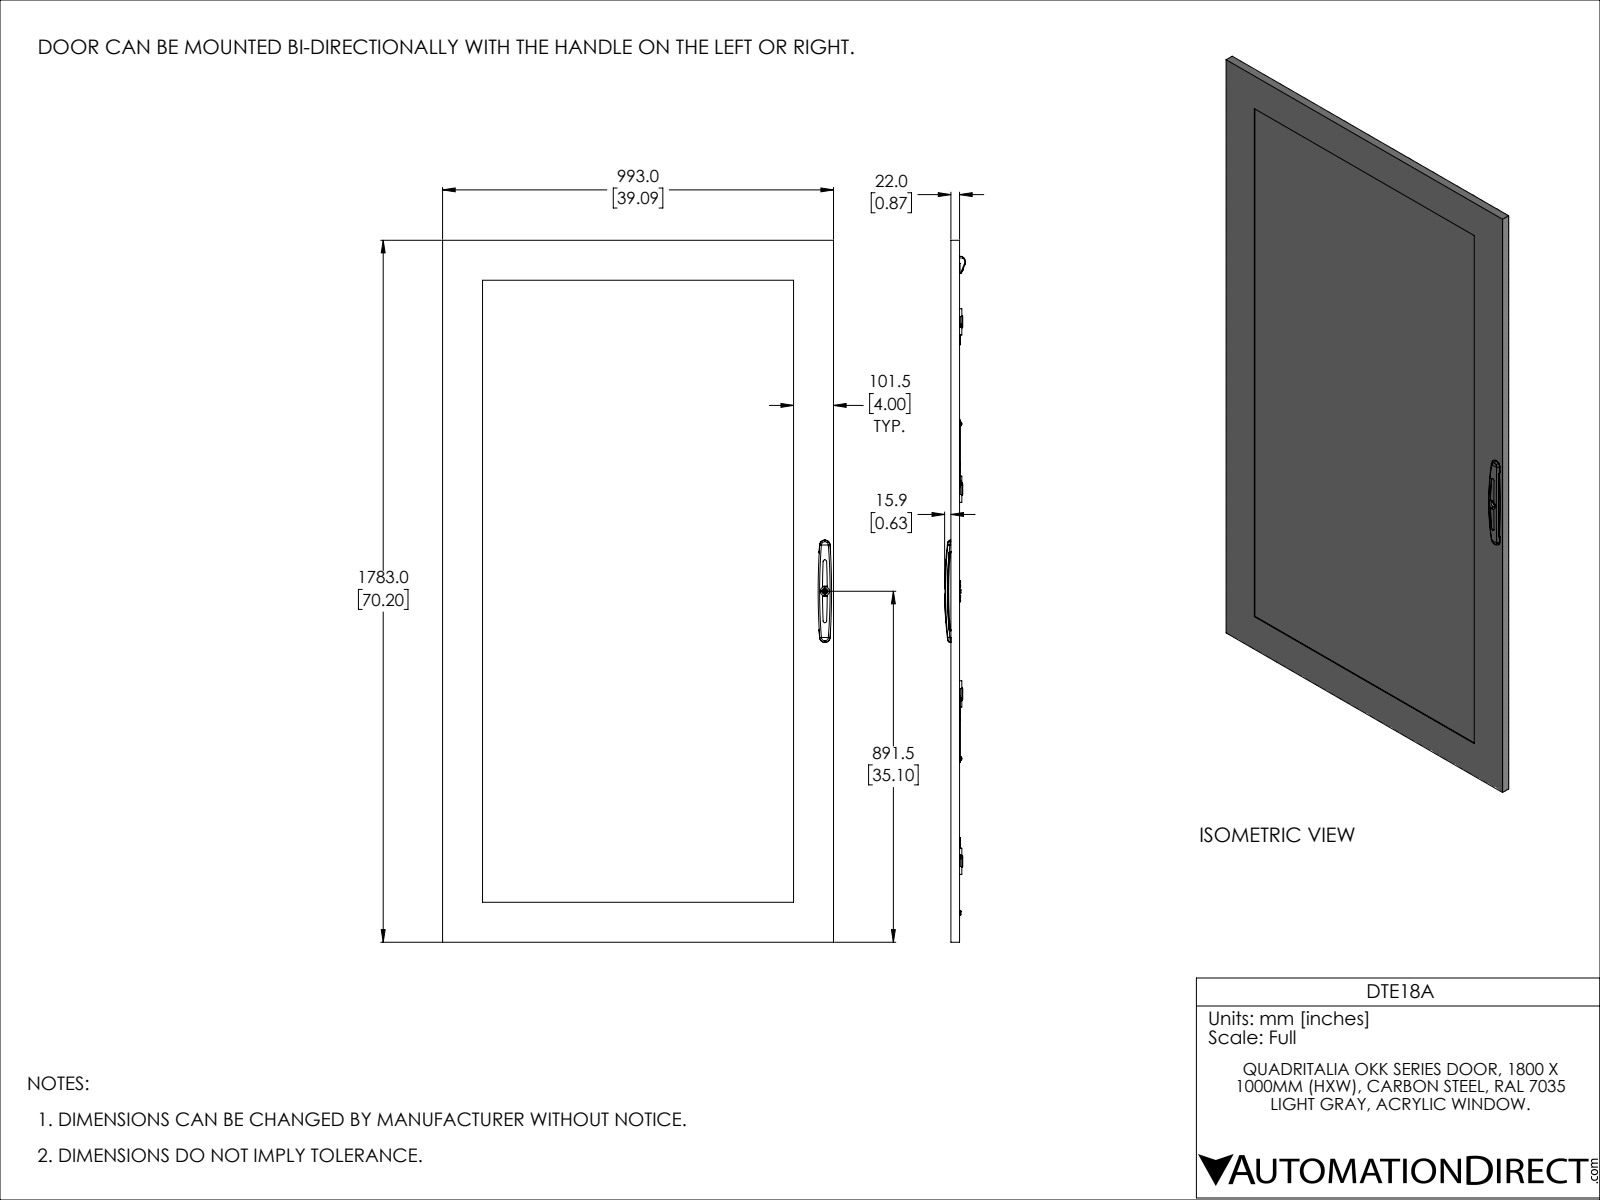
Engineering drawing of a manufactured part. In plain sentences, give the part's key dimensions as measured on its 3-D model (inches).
The part is named "DTE18A". Its 3-D file was written by "SolidWorks 2021 (CONFIG_CONTROL_DESIGN)". It is 102 solids with 3645 faces: 1763 planar, 1253 cylindrical and 629 other. Overall it measures 70.197 by 39.094 by 2.091 inches. Its volume is 487.1 cubic inches and its surface area 8 092 square inches. Round holes: 152 of diameter 0.167, 29 of diameter 0.315, 20 of diameter 0.354, 8 of diameter 0.01, 8 of diameter 0.194, 8 of diameter 0.197, 6 of diameter 0.194, 4 of diameter 0.244, 4 of diameter 0.276, 3 of diameter 0.205, 2 of diameter 0.134, 2 of diameter 0.169. Round bosses or shafts: 21 of diameter 0.276, 17 of diameter 0.236, 14 of diameter 0.283, 10 of diameter 0.394, 9 of diameter 0.197, 8 of diameter 0.193, 2 of diameter 0.472, 2 of diameter 0.315. Partial cylindrical surfaces (rounded edges, fillets, slot ends): 74 of radius 0.012, 70 of radius 0.039, 36 of radius 0.059, 33 of radius 0.02, 28 of radius 0.098, 16 of radius 0.177, 15 of radius 0.079, 14 of radius 0.227. The main face-to-face distances are 0.157, 0.079, 0.236, 0.059, 0.728, 0.787, 0.669, 0.866, 0.63, 33.858. The hole center spacings are 0.984, 1.969, 2.953, 3.937, 4.921, 5.906, 6.89, 7.874.
